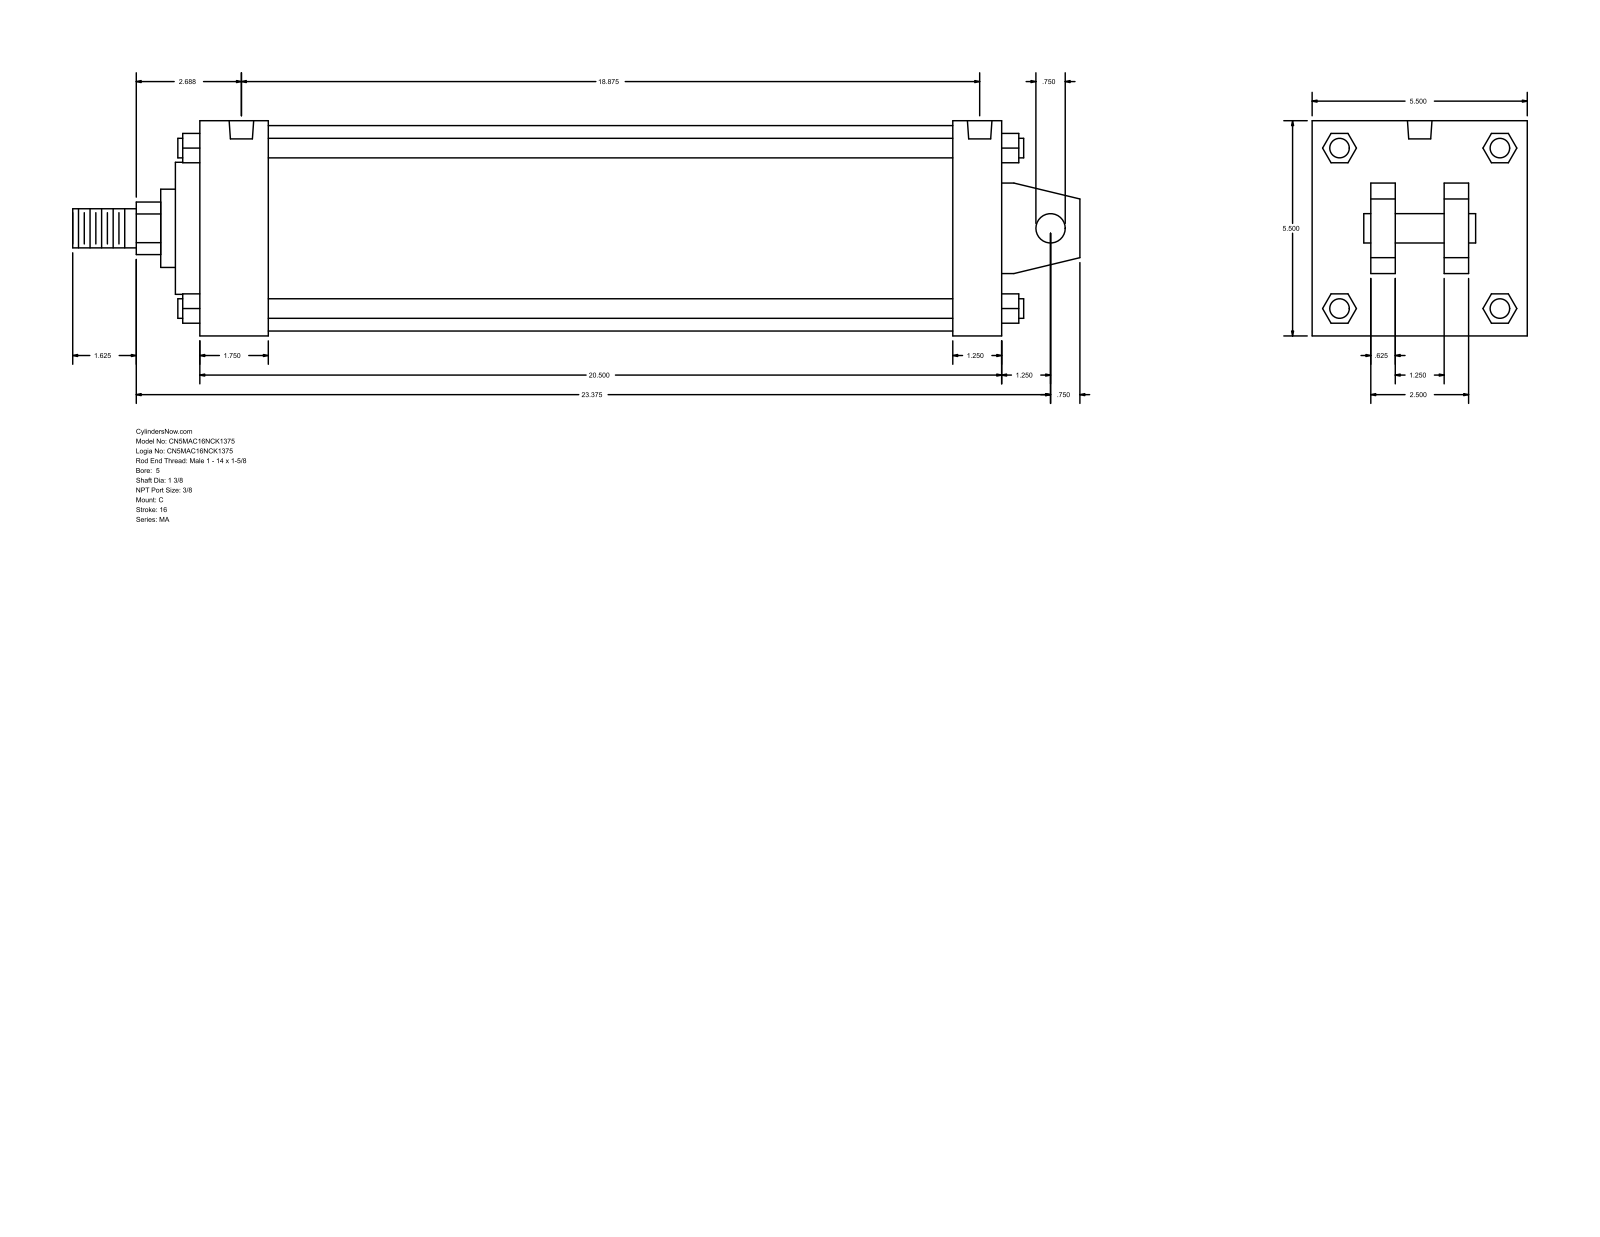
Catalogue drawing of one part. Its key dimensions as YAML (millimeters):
part_name: "MA_C__0500_1.375"
step_written_by: "GSSL Pune (CONFIG_CONTROL_DESIGN)"
units: millimeters
bodies: {solids: 0, faces: 141, planar: 109, cylindrical: 32, other: 0}
overall_size: [654.05, 139.7, 139.7]
round_holes:
  - {diameter: 11.11, count: 4}
  - {diameter: 15.93, count: 2}
round_bosses_or_shafts:
  - {diameter: 12.7, count: 4}
  - {diameter: 133.35, count: 1}
  - {diameter: 85.72, count: 1}
  - {diameter: 50.8, count: 1}
  - {diameter: 34.92, count: 1}
  - {diameter: 25.4, count: 1}
  - {diameter: 19.05, count: 1}
partial_cylinders:
  - {radius: 17.06, count: 1}
face_to_face_distances: [139.7, 520.71, 15.87, 488.96, 31.75, 44.45, 444.51, 476.26, 53.97, 38.1]
hole_center_spacings: [4.77, 469.89, 474.66, 479.43]
